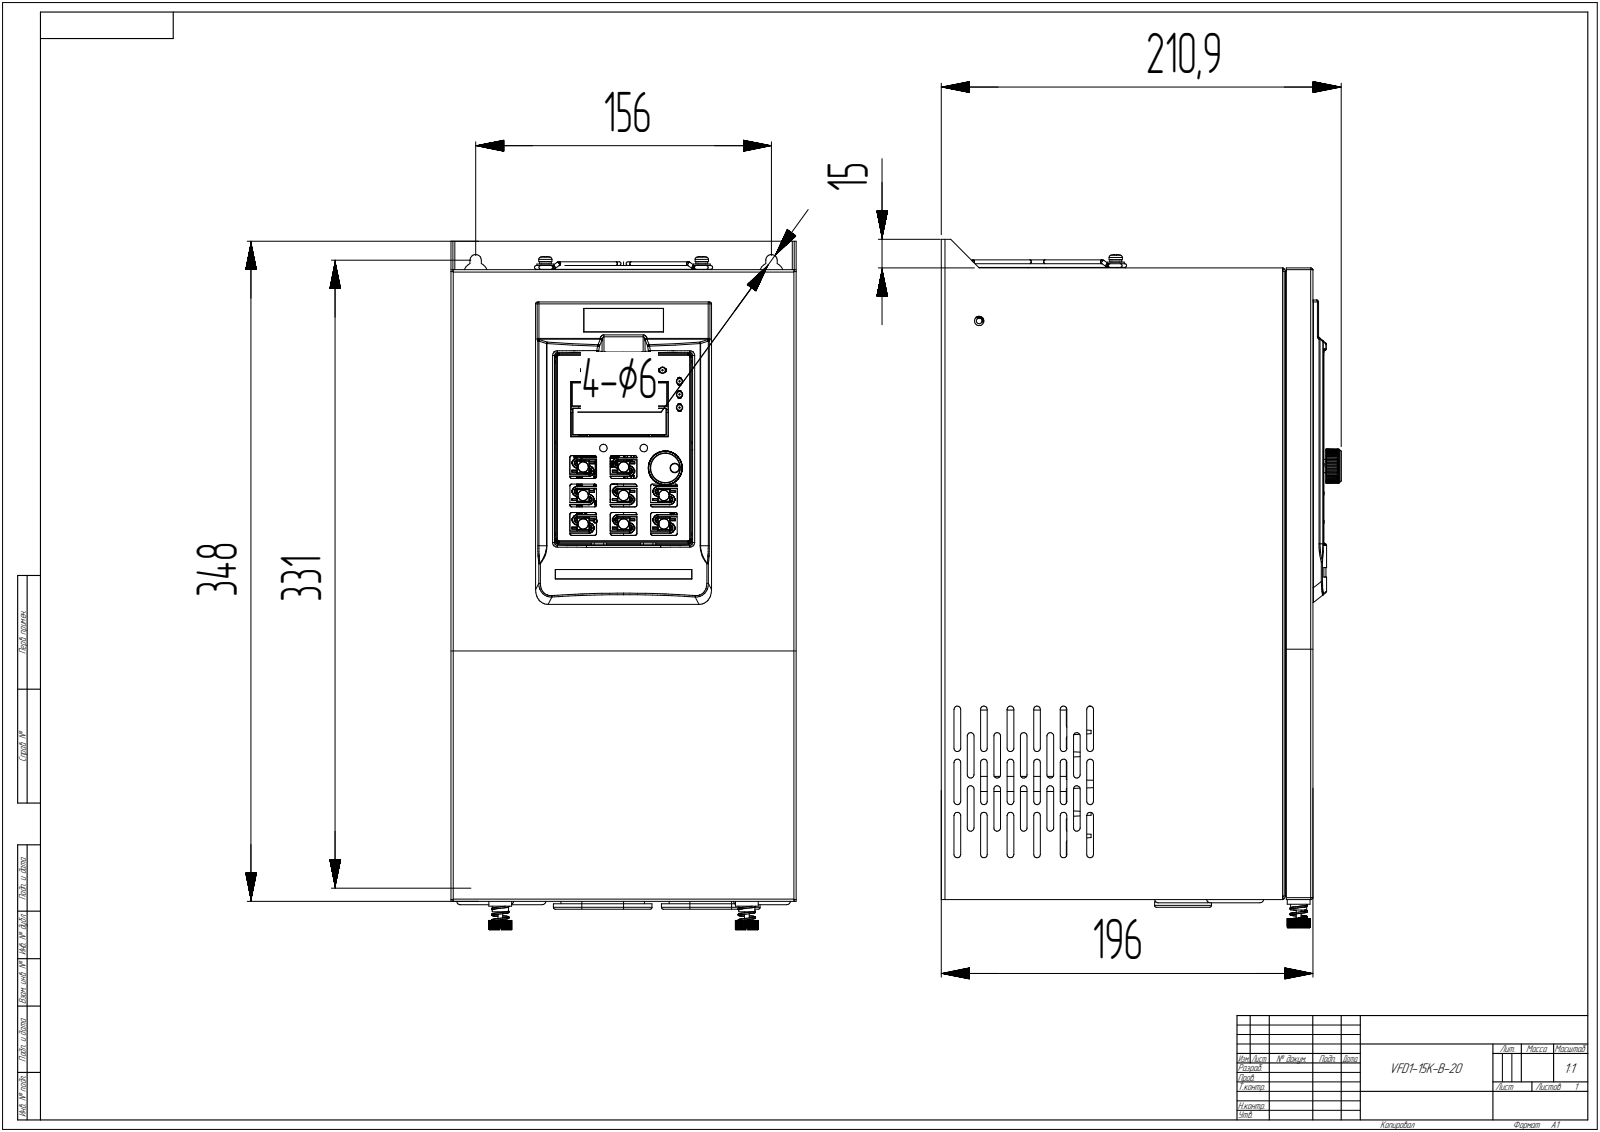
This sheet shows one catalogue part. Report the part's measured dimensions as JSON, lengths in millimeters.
{"part_name": "PRT0021", "step_written_by": "CREO PARAMETRIC BY PTC INC, 2020074 (CONFIG_CONTROL_DESIGN)", "units": "millimeters", "bodies": {"solids": 1, "faces": 6177, "planar": 3226, "cylindrical": 1947, "other": 1004}, "overall_size": [363, 210.9, 182], "volume_mm3": 10270000, "surface_area_mm2": 1323000, "round_holes": [[5.4, 18], [4.1, 11], [4.3, 11], [5, 9], [4.5, 8], [2, 6], [3, 6], [4, 6], [5.38, 6], [2.5, 4], [19, 3], [22, 3]], "round_bosses_or_shafts": [[1.2, 19], [0.5, 14], [9, 13], [7, 12], [4, 12], [6.3, 11], [2, 11], [5, 10]], "partial_cylinders_radius": [[1.75, 212], [0.5, 130], [1, 100], [1.25, 48], [0.34, 35], [2, 30], [1.5, 19], [3, 12]], "face_to_face_distances": [1, 180, 181, 195, 194, 85, 110, 182, 55.5, 54.5], "hole_center_spacings": [58.34, 82.5, 343.54, 13.79, 14.14, 15.23, 20.01, 25.5]}
